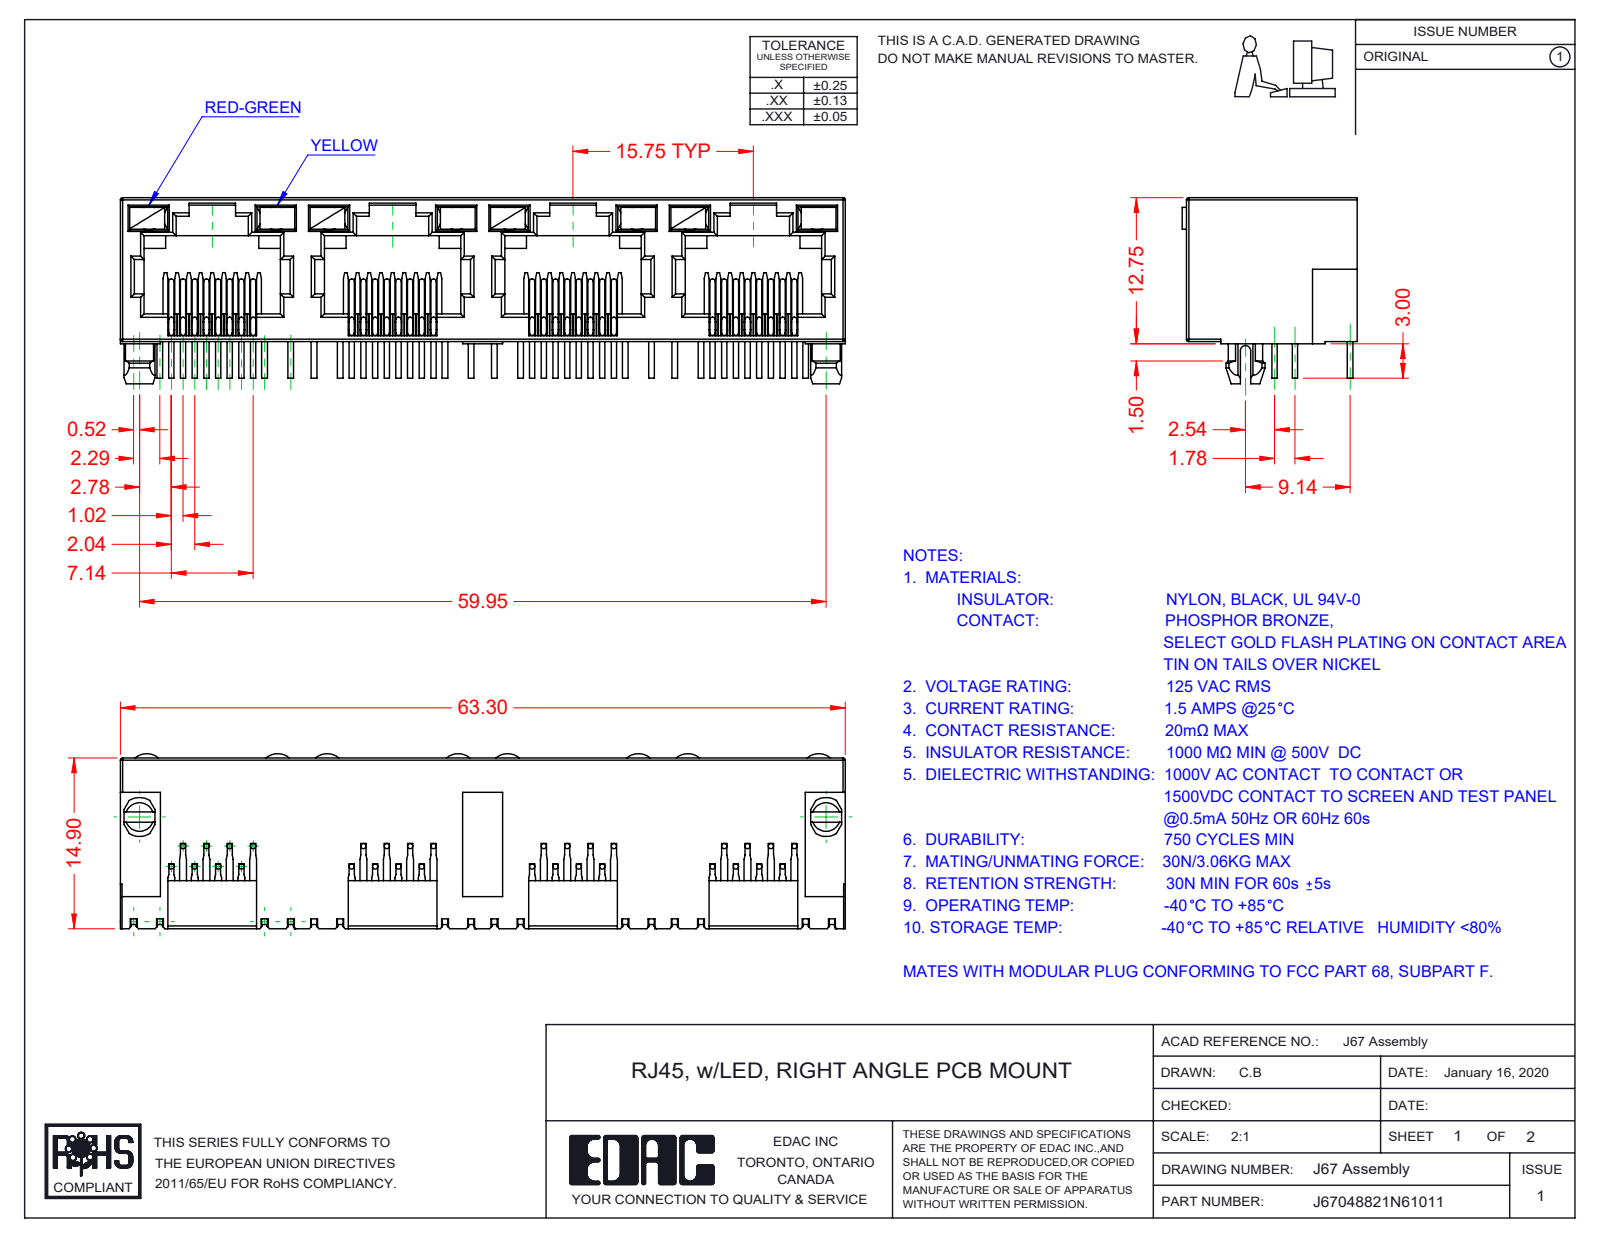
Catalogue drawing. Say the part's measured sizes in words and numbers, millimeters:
The part is named "67 LED LH_6-Red-Green; 67 Insulator; 67 LED RH_1-Yellow; J67048822N61011 (+1 more)". Its 3-D file was written by "SolidWorks 2016 (CONFIG_CONTROL_DESIGN)". It is 41 solids with 2473 faces: 1781 planar, 484 cylindrical and 208 other. Overall it measures 63.3 by 16.25 by 15.28 millimeters. Its volume is 5 159 cubic millimeters and its surface area 11 573 square millimeters. Round bosses or shafts: 96 of diameter 0.46. Partial cylindrical surfaces (rounded edges, fillets, slot ends): 66 of radius 0.2, 29 of radius 0.3, 9 of radius 0.45, 8 of radius 1.55, 2 of radius 1.5, 2 of radius 1.7, 1 of radius 0.35, 1 of radius 1. The main face-to-face distances are 0.5, 12.55, 1.89, 0.89, 10, 15.75, 1, 1.39, 11, 11.89.
